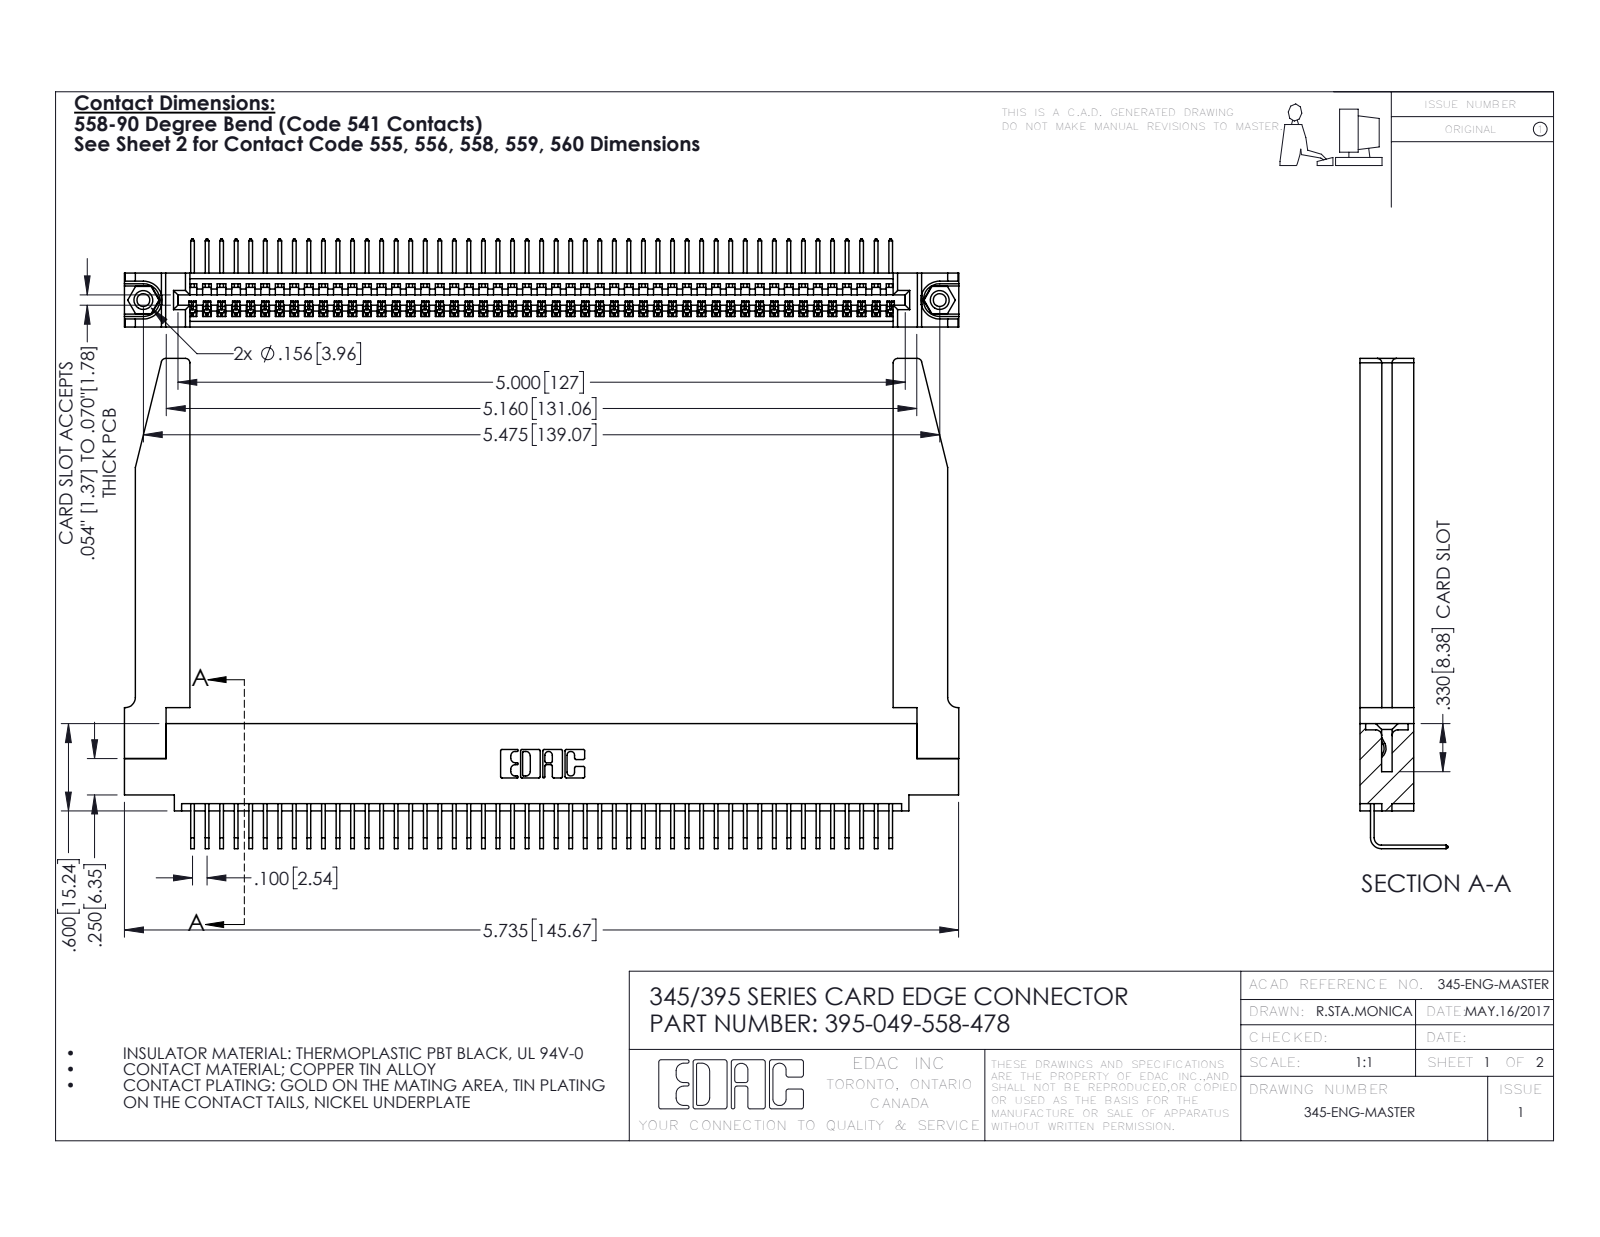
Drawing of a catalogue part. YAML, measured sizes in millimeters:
part_name: "345-250-001_345-250-001-102; 345-220-078_345-220-078; 345-292-001_558 Tail - 2; 395-049-558-478 (+1 more)"
step_written_by: "SolidWorks 2016 (CONFIG_CONTROL_DESIGN)"
units: millimeters
bodies: {solids: 54, faces: 3304, planar: 2284, cylindrical: 968, other: 52}
overall_size: [145.7, 85.6, 15.4]
volume: 21760
surface_area: 26570
round_holes:
  - {diameter: 2.3, count: 2}
  - {diameter: 3.2, count: 2}
  - {diameter: 4, count: 2}
  - {diameter: 1.6, count: 1}
round_bosses_or_shafts:
  - {diameter: 3.9, count: 2}
partial_cylinders:
  - {radius: 0.2, count: 98}
  - {radius: 0.3, count: 22}
  - {radius: 0.8, count: 8}
  - {radius: 0.2, count: 6}
  - {radius: 0.8, count: 6}
  - {radius: 0.7, count: 3}
  - {radius: 0.8, count: 2}
  - {radius: 1, count: 2}
face_to_face_distances: [9.4, 1.8, 7.6, 2.5, 6.9, 0.6, 5.1, 5.7, 3.8, 3.8]
hole_center_spacings: [6.9, 133.1, 139.1]
